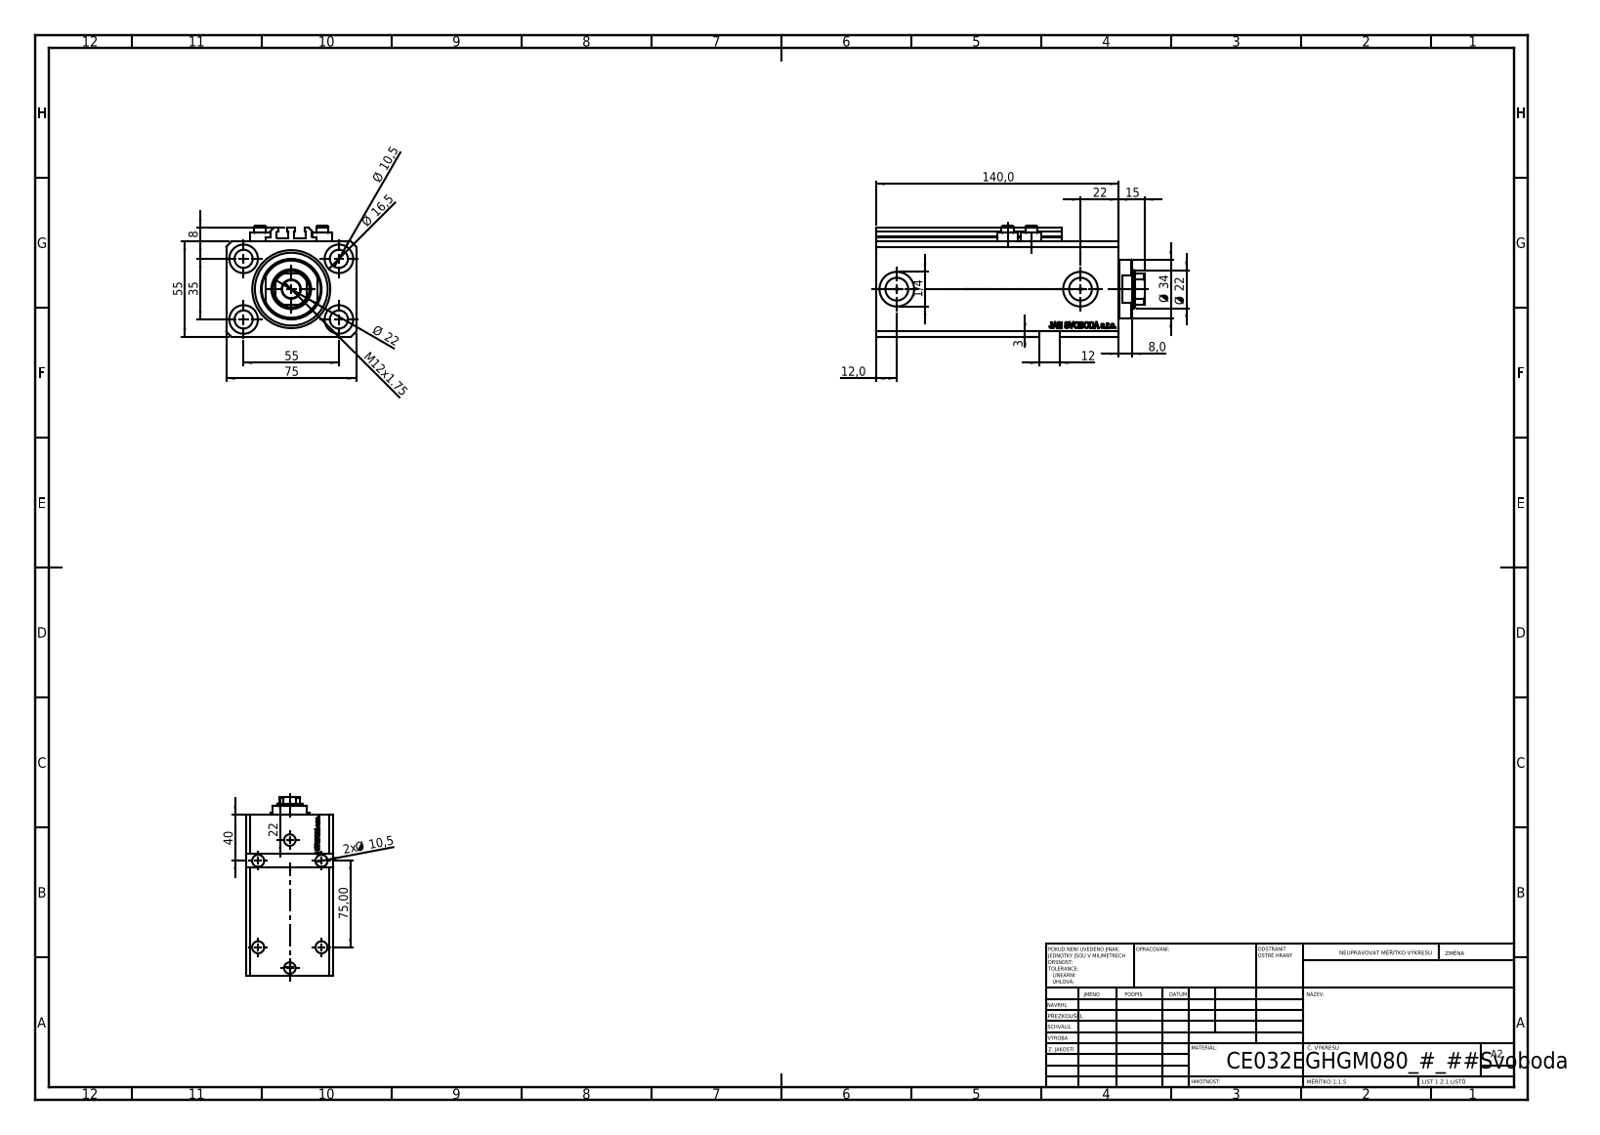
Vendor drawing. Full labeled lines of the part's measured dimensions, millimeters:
Part name (STEP PRODUCT): V250CE_C_VCP; ALLEN BOLT V250CE; V250CE_VC_E; V250CE_E_Body
STEP written by: SolidWorks 2019 (CONFIG_CONTROL_DESIGN)
Units: millimetres
Bodies: 8 solids, 1084 faces (514 planar, 146 cylindrical, 424 other)
Overall size (bounding box): 155 × 75 × 64
Volume: 485 219 mm³ · Surface area: 115 303 mm²
Round holes (diameter × count): ⌀10.5 ×9, ⌀1.25 ×4, ⌀4 ×4, ⌀16.5 ×4, ⌀10 ×2, ⌀13.16 ×2, ⌀20 ×2, ⌀22 ×1, ⌀32 ×1, ⌀45 ×1
Round bosses / shafts (diameter × count): ⌀11.6 ×4, ⌀7 ×4, ⌀34 ×1
Partial cylindrical surfaces — rounded edges, fillets, slot ends (radius × count): R0.2 ×10, R10.5 ×1
Main face-to-face distances: 55, 75, 15, 140, 125, 3, 9.9, 57, 115.1, 130.1
Hole centre spacings: 32.6, 32.87, 55, 96.98, 13.6, 14.09, 25.81, 32.58
